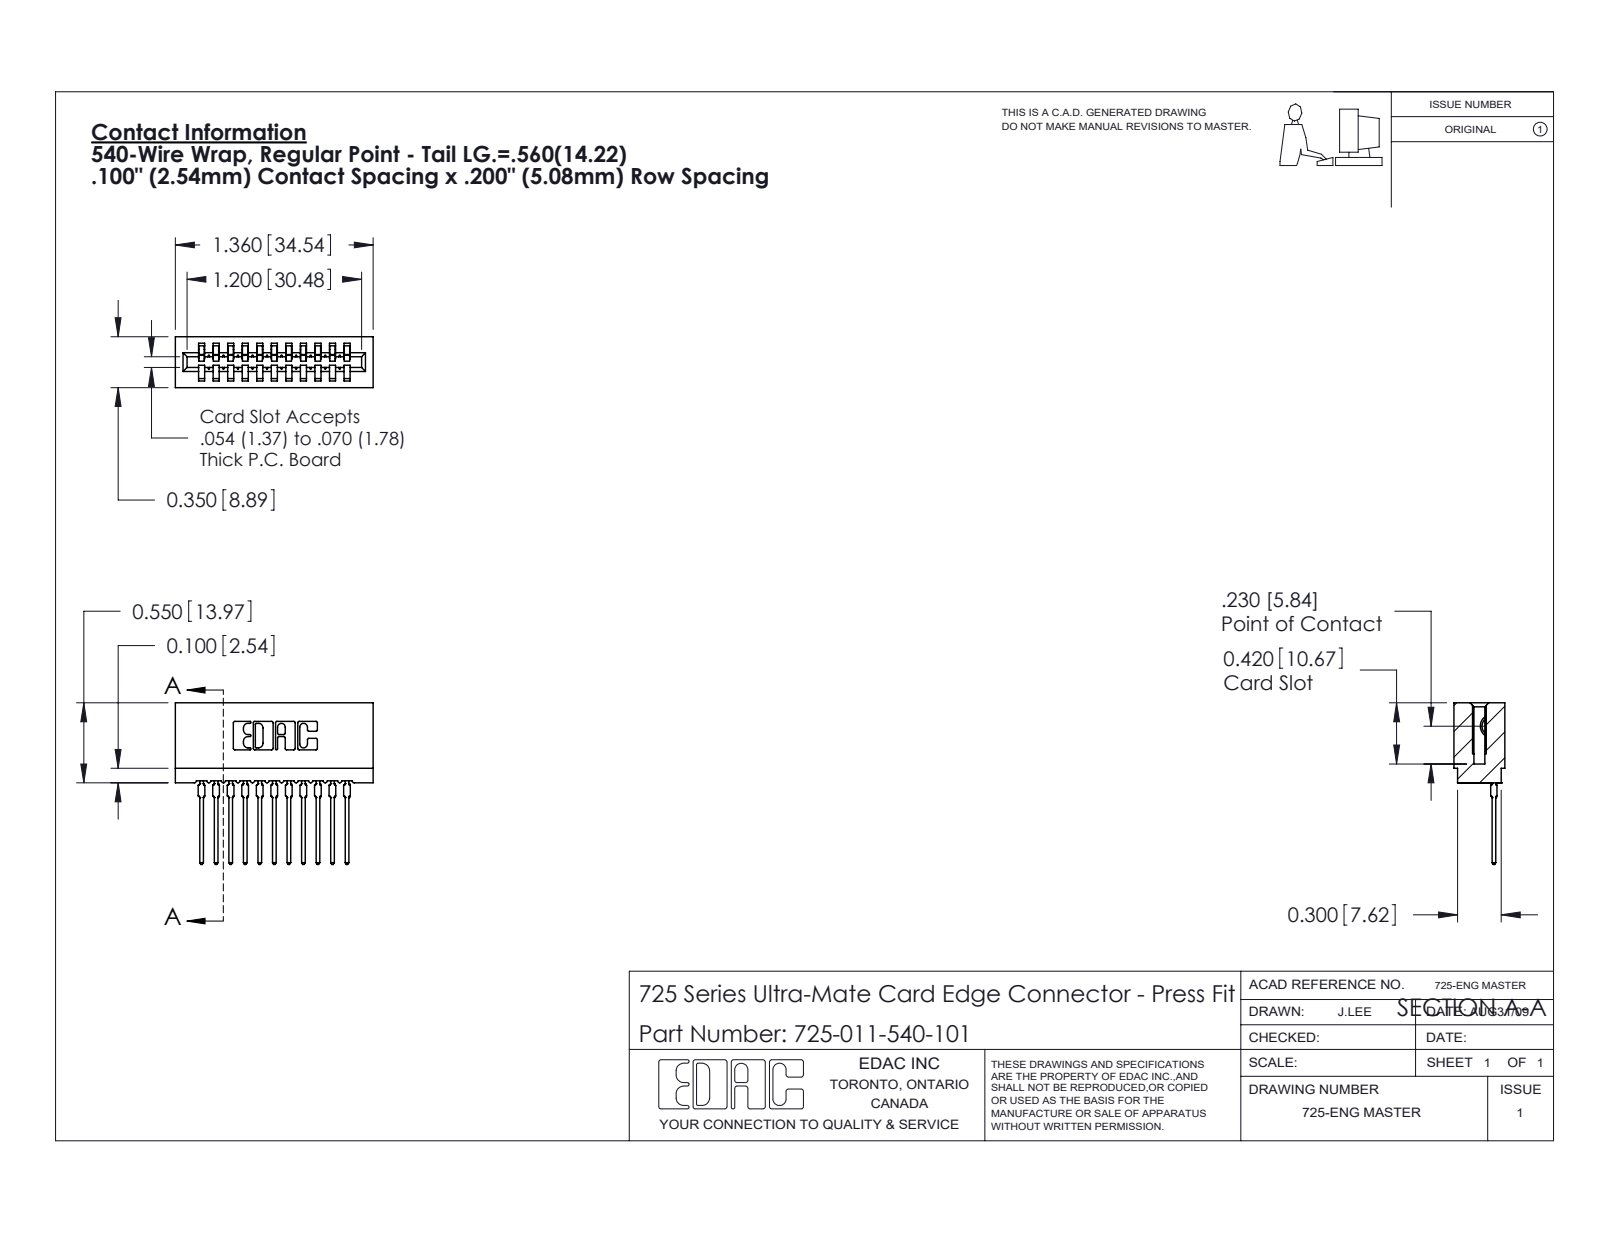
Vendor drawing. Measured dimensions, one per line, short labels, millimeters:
name: 725-011-540-101; 745-292-001_540; 725 Part_Insulator Option - 01
written by: SolidWorks 2020 (CONFIG_CONTROL_DESIGN)
unit: mm
bodies: 12 solids, 1327 faces (792 planar, 249 cylindrical, 286 other)
size: 34.5 × 28.2 × 8.9
volume: 2 820 mm³; area: 4 987 mm²
rounds: 22× R0.3, 22× R0.4, 22× R0.5, 6× R0.2, 6× R0.8, 4× R0.1, 4× R0.3, 3× R0.7
face distances: 2.5, 5.1, 7.6, 10.2, 12.7, 4, 1.5, 1.1, 3.6, 6.6
